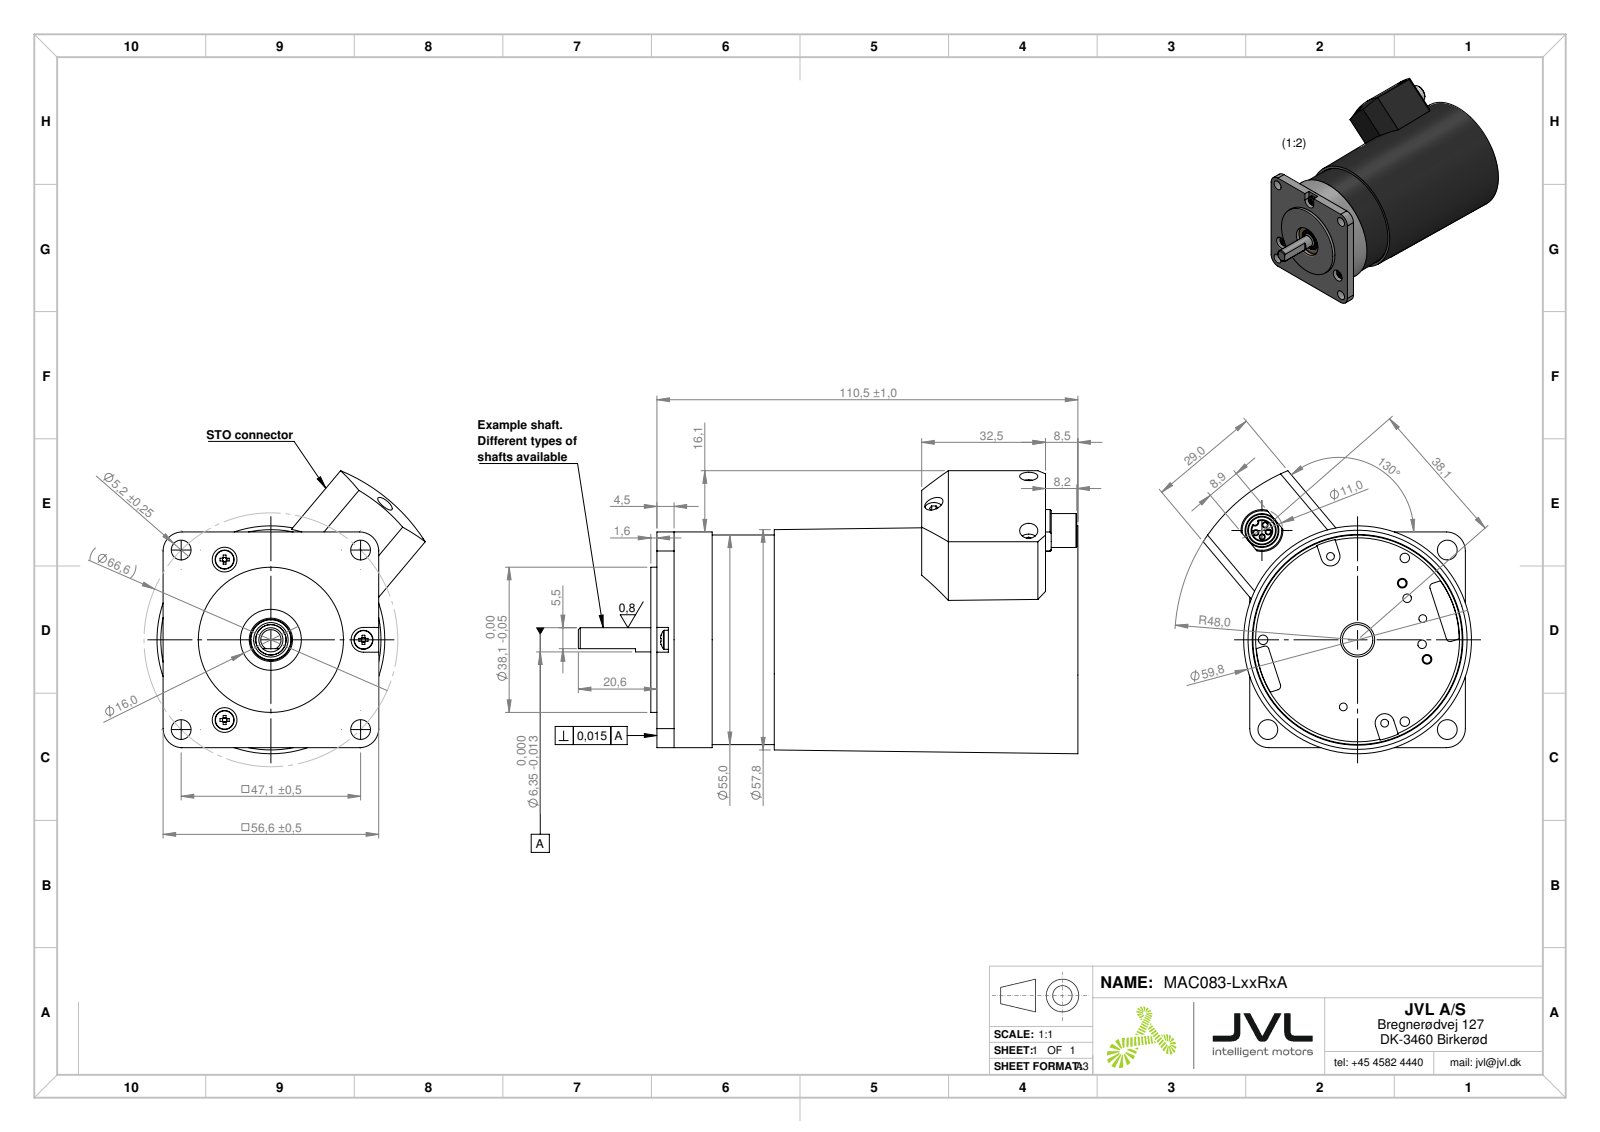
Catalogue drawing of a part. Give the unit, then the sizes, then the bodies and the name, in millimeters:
Units: millimetres
Overall size (bounding box): 131.12 × 74.27 × 70.42
Round holes (diameter × count): ⌀2.05 ×6, ⌀1.2 ×4, ⌀5.2 ×4, ⌀2.5 ×3, ⌀4.8 ×3, ⌀6.5 ×2, ⌀7.1 ×1, ⌀8 ×1, ⌀9 ×1, ⌀10 ×1, ⌀10.76 ×1, ⌀11.37 ×1
Round bosses / shafts (diameter × count): ⌀5 ×3, ⌀2.5 ×3, ⌀2.25 ×2, ⌀56.6 ×1, ⌀56 ×1, ⌀55 ×1, ⌀38.1 ×1, ⌀28 ×1
Partial cylindrical surfaces — rounded edges, fillets, slot ends (radius × count): R1 ×4, R5 ×4, R0.2 ×2, R2.5 ×2, R4 ×2, R0.8 ×1, R3.25 ×1, R5.5 ×1
Main face-to-face distances: 20.8, 53.7, 32.9, 6, 14.8, 47.7, 55.3, 49.3, 34.5, 1.6
Hole centre spacings: 33.3, 42.52, 47.1, 24.8, 36.34, 42.96, 0.51, 1.69
Volume: 137 914 mm³ · Surface area: 58 906 mm²
Bodies: 20 solids, 668 faces (272 planar, 156 cylindrical, 240 other)
Part name (STEP PRODUCT): Shaft variants MAC083-320 (base)_Ø6.35 L20.6 D-shaped; pan head cross recess screw_din_DIN EN ISO 7045 - M2.5 x 8 - Z - 8N; MM0315 MAC50-140 Housing; MAC083-320 (base)_MAC083 (+3 more)
STEP written by: SolidWorks 2023 (AUTOMOTIVE_DESIGN)
